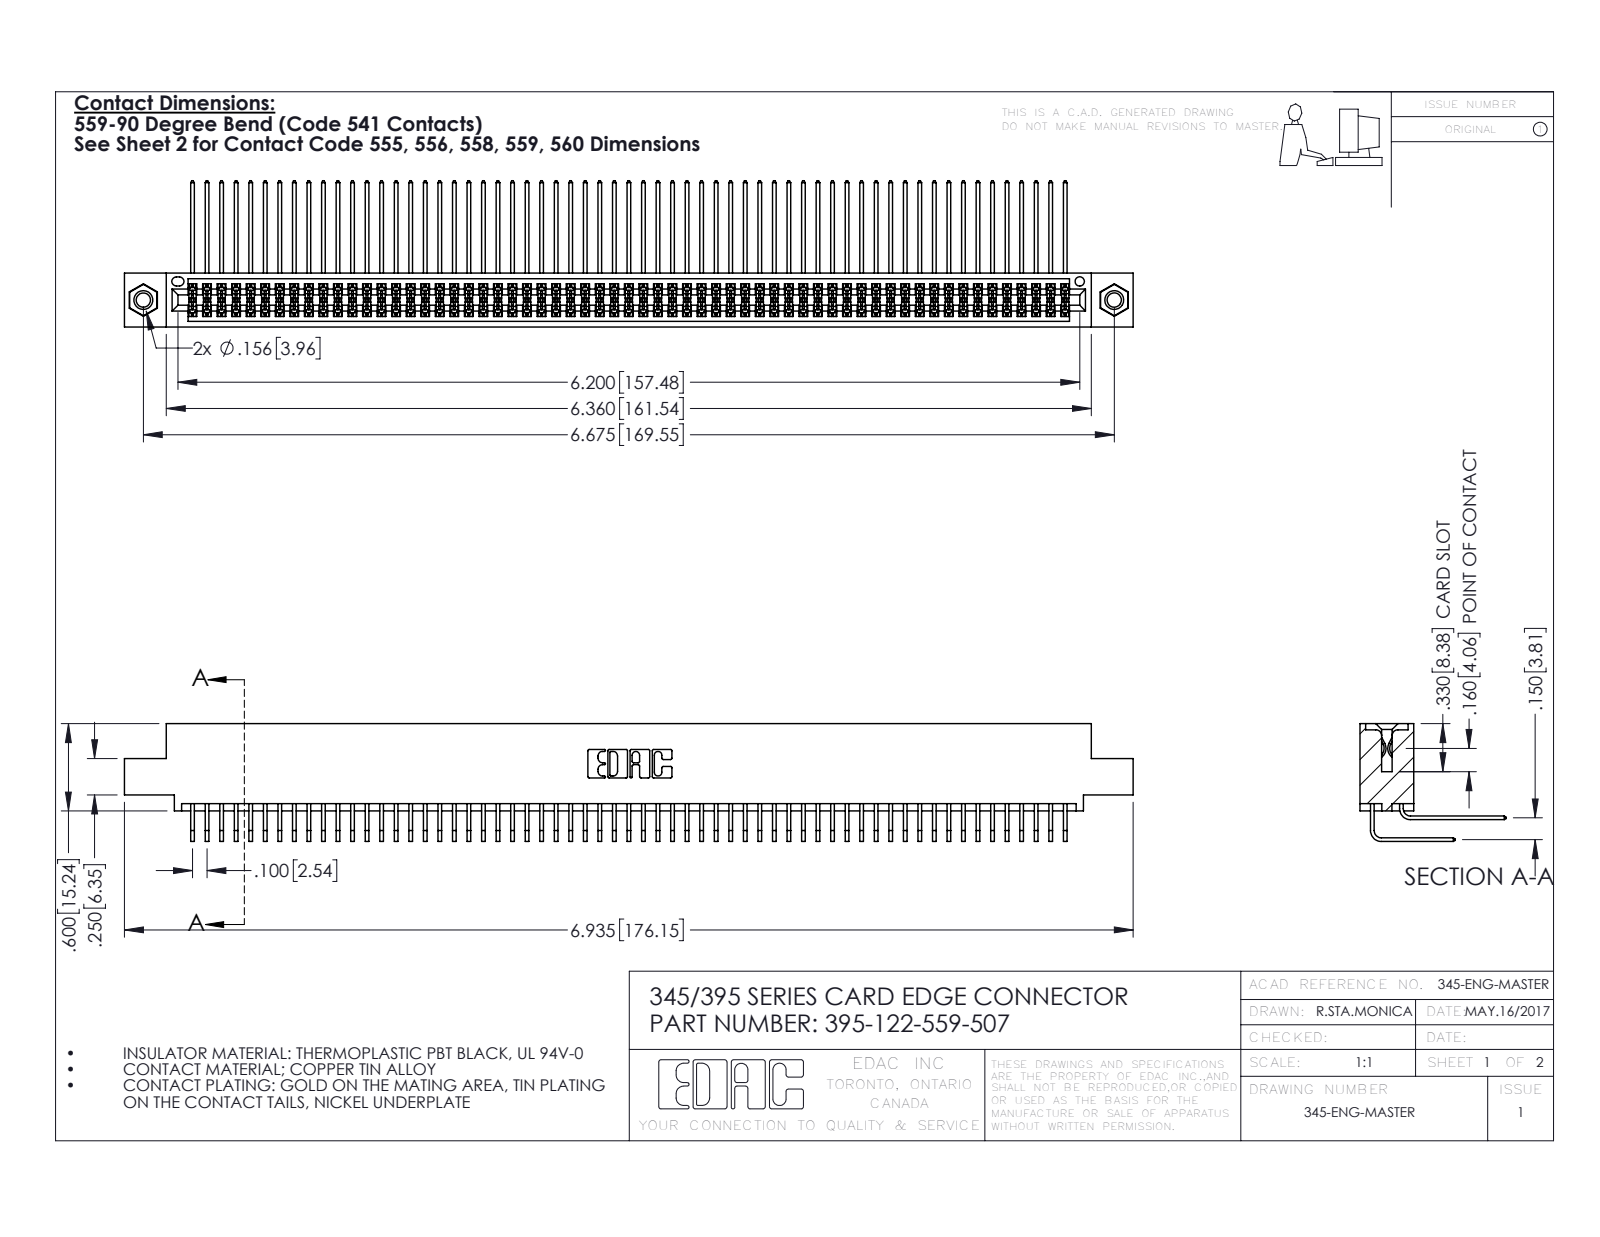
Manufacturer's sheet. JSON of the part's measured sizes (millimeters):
{"part_name": "345-250-001_345-250-005-103; 345 Part_0.110 Offset - 0.156 Dia-TI; 395-122-559-507; 345-292-001_558 559 Tail - 1 (+1 more)", "step_written_by": "SolidWorks 2016 (CONFIG_CONTROL_DESIGN)", "units": "millimeters", "bodies": {"solids": 125, "faces": 6534, "planar": 4386, "cylindrical": 2132, "other": 16}, "overall_size": [176.1, 25.5, 20.5], "volume_mm3": 17910, "surface_area_mm2": 30260, "round_holes": [[2.5, 2], [3.2, 2], [4, 2], [1.6, 1]], "round_bosses_or_shafts": [[3.9, 2]], "partial_cylinders_radius": [[0.2, 183], [0.3, 22], [0.2, 6], [0.8, 6], [0.7, 3], [0.4, 2], [0.5, 2], [0.6, 2]], "face_to_face_distances": [1.8, 7.6, 5.1, 9.4, 2.5, 6.9, 0.6, 5.7, 4.4, 3.8], "hole_center_spacings": [6.9, 163.6, 169.5]}
